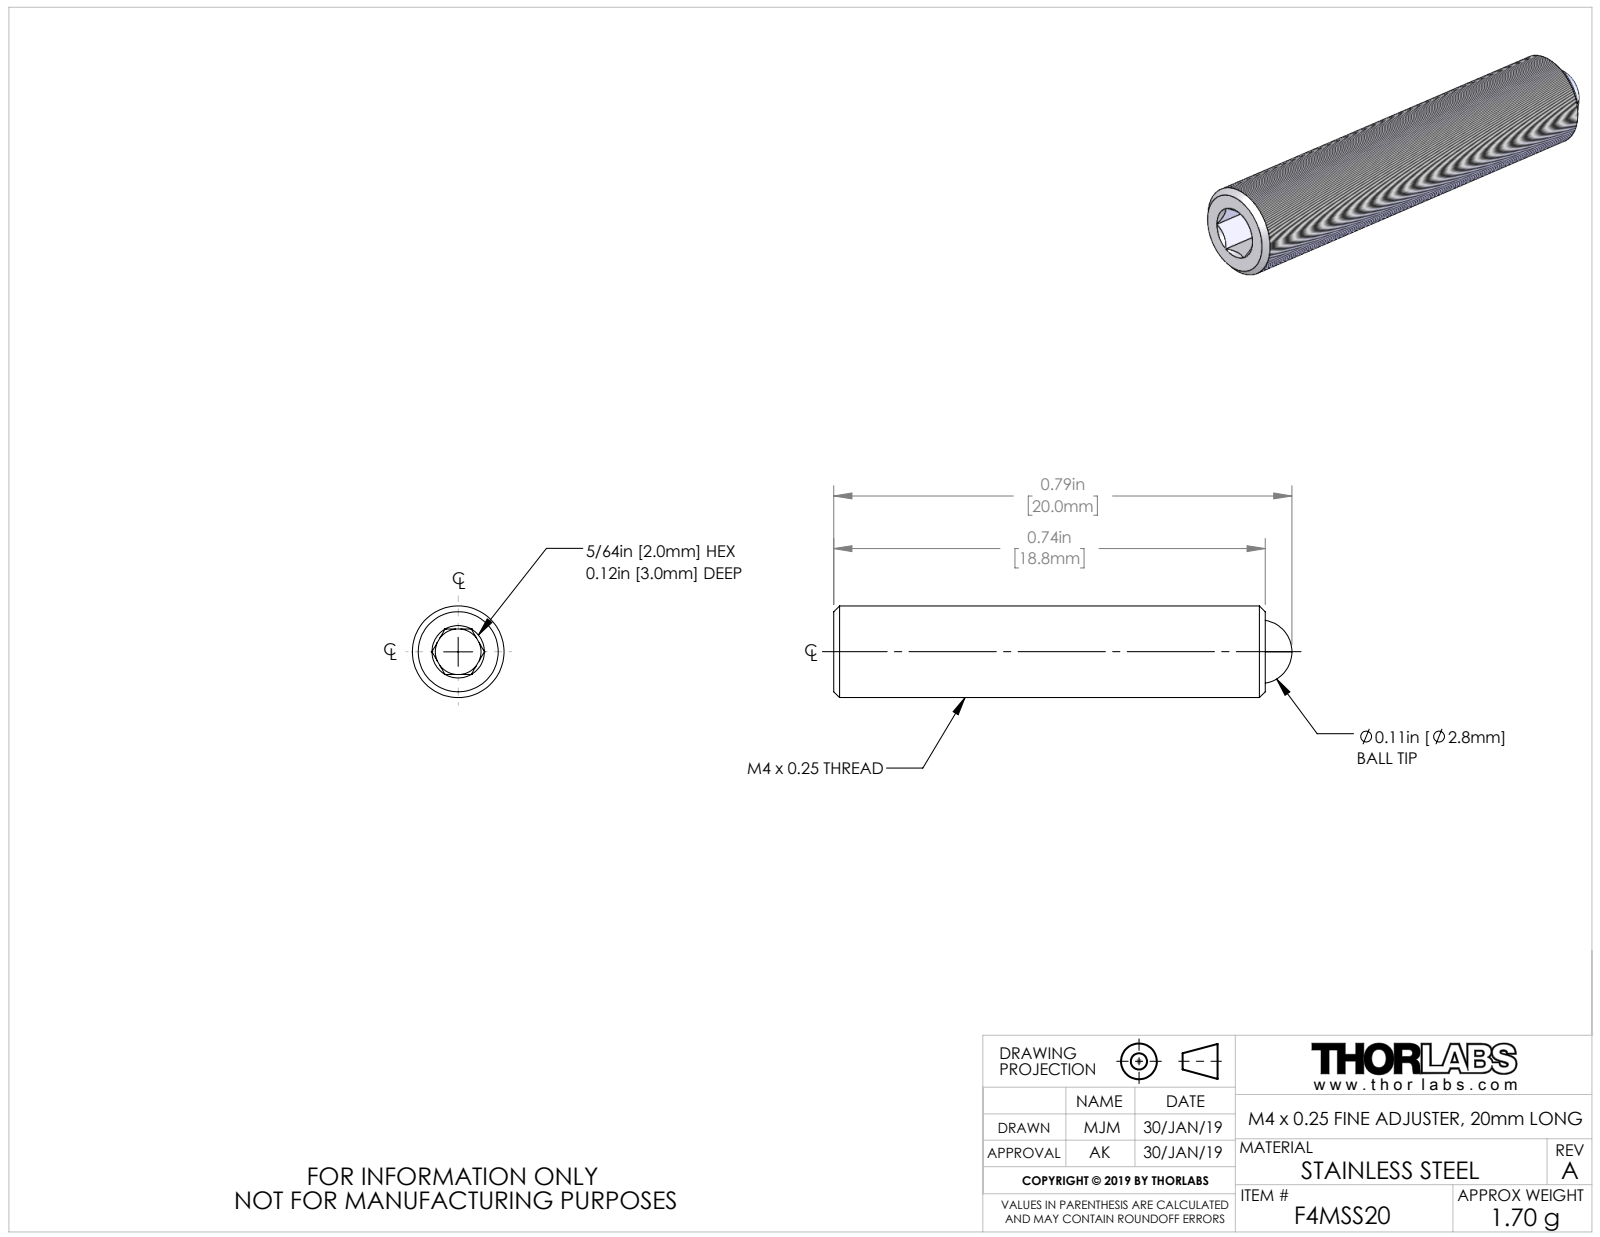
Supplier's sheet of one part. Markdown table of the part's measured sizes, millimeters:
| quantity | value |
| --- | --- |
| part name | TTN174703-E0W |
| STEP written by | SolidWorks 2018 (AUTOMOTIVE_DESIGN) |
| units | millimeters |
| bodies | 2 solids, 45 faces (20 planar, 6 cylindrical, 19 other) |
| overall size | 20 × 4 × 4 |
| volume | 230 mm³ |
| surface area | 318 mm² |
| round holes (diameter × count) | 2 × 1, 2.8 × 1 |
| round bosses / shafts (diameter × count) | 4 × 1 |
| main face-to-face distances | 2, 18.8, 15.8, 3 |
